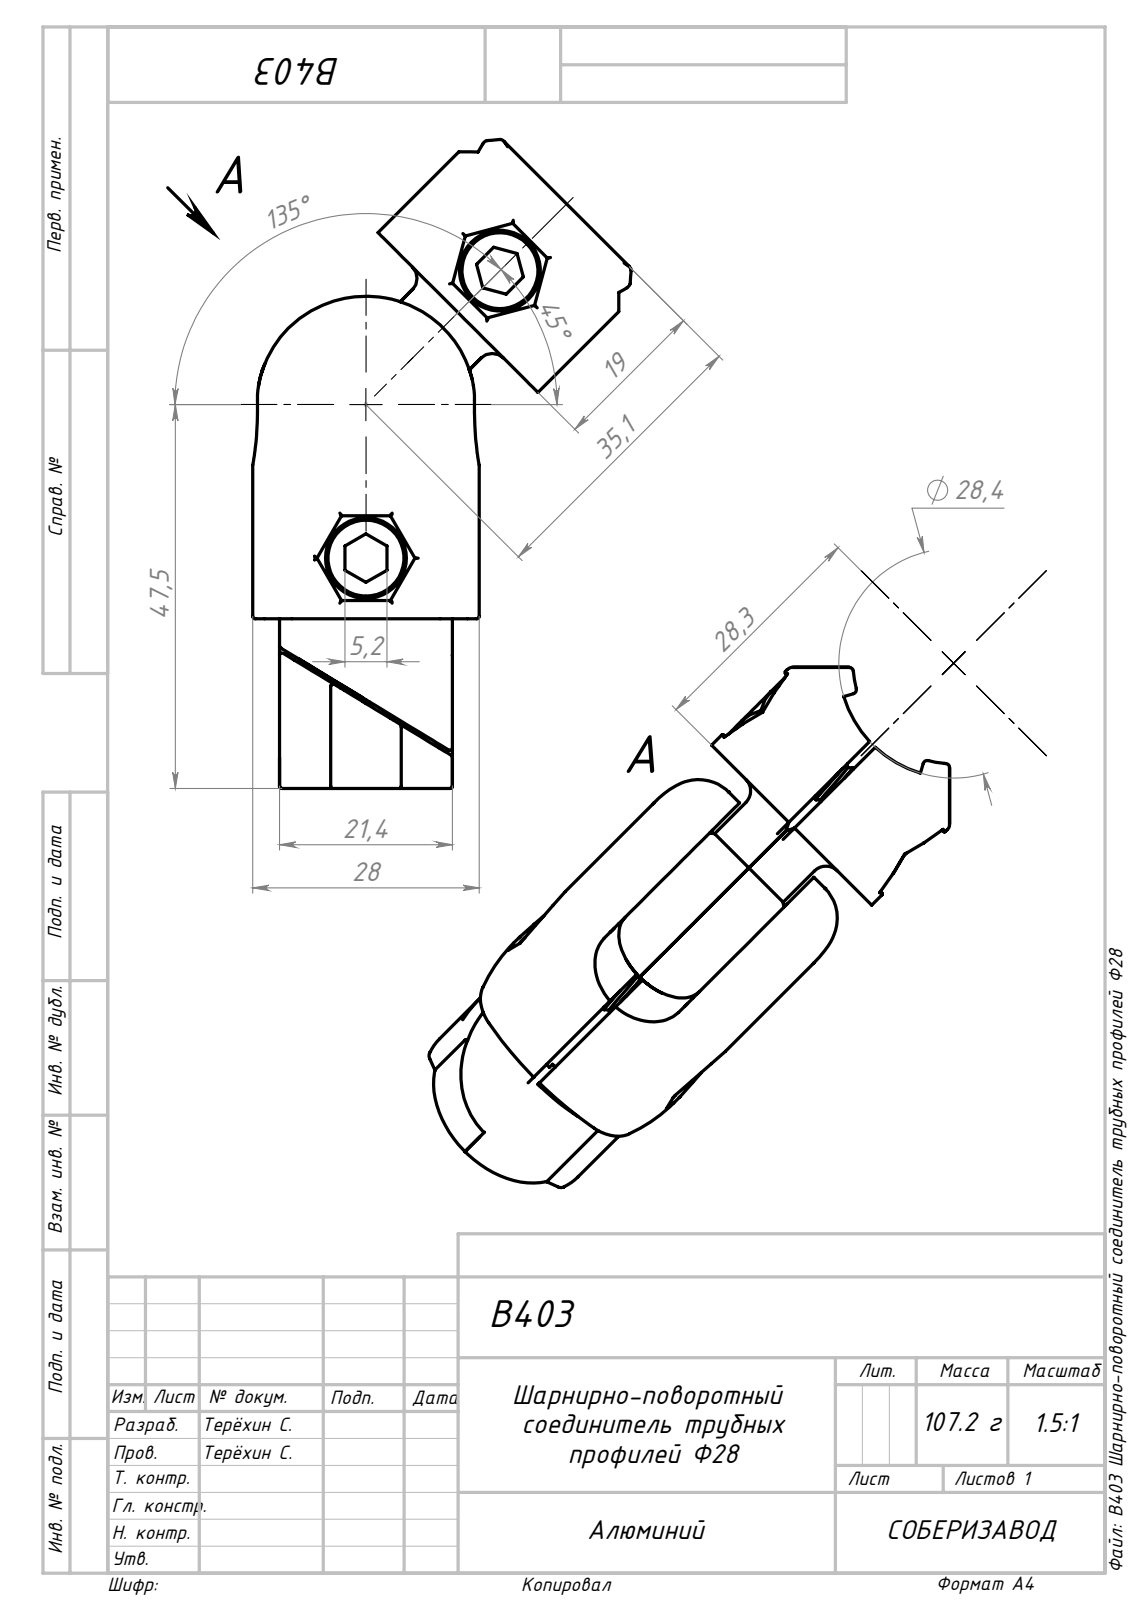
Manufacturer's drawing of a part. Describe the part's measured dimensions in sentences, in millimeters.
The part is named "B403 Шарнирно-поворотный соединитель трубных профилей Ф28". Its 3-D file was written by "SolidWorks 2022 (AUTOMOTIVE_DESIGN)". It is 8 solids with 620 faces: 162 planar, 196 cylindrical and 262 other. Overall it measures 76.13 by 55.02 by 28 millimeters. Its volume is 36 857 cubic millimeters and its surface area 20 343 square millimeters. Round holes: 2 of diameter 5.2, 2 of diameter 6.5. Round bosses or shafts: 2 of diameter 10, 2 of diameter 6, 1 of diameter 28, 1 of diameter 21.4, 1 of diameter 12. Partial cylindrical surfaces (rounded edges, fillets, slot ends): 22 of radius 1, 20 of radius 0.5, 8 of radius 0.3, 4 of radius 5, 4 of radius 37, 2 of radius 6.5, 1 of radius 12, 1 of radius 12.1. The main face-to-face distances are 0.5, 7, 6, 6.5, 1, 13, 4, 2, 10.28, 5. The hole center spacings are 39.25.
